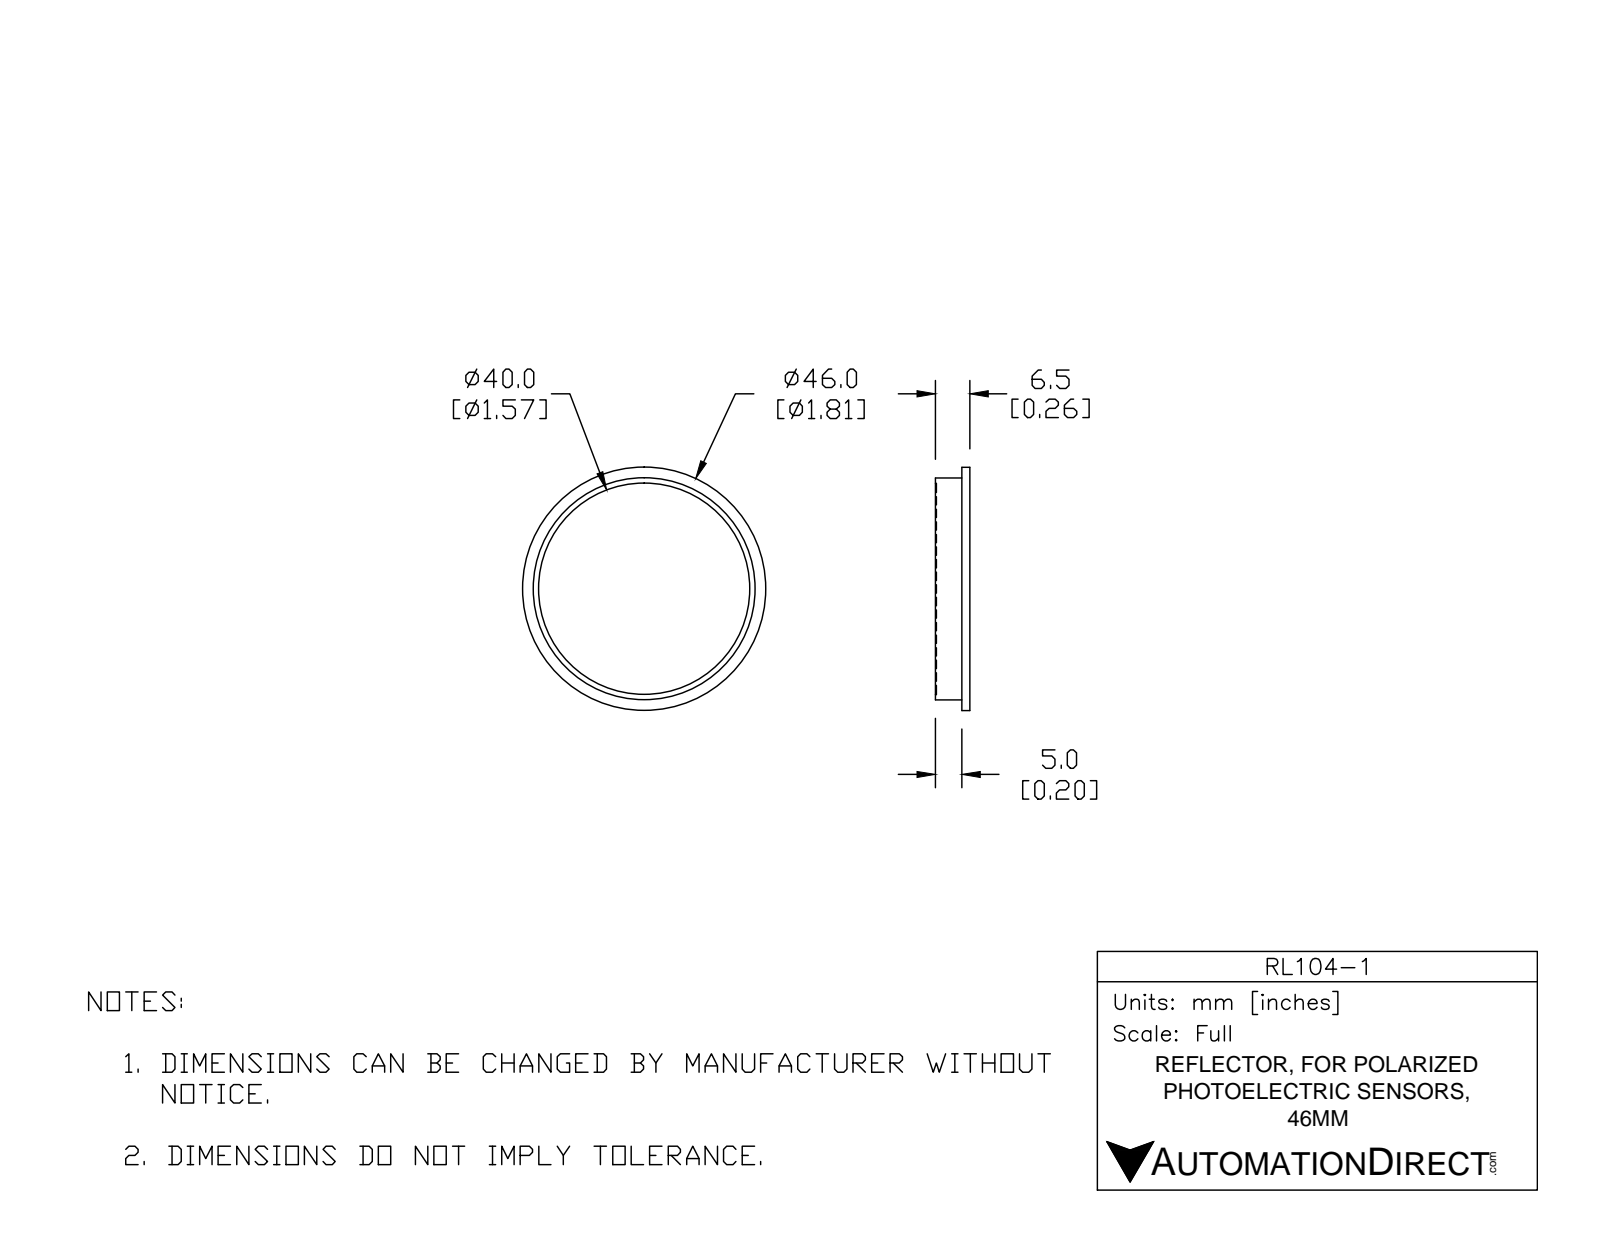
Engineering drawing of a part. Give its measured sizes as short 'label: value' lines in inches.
name: RL-104-1
written by: SolidWorks 2017 (AUTOMOTIVE_DESIGN)
unit: in
bodies: 1 solid, 10 faces (4 planar, 6 cylindrical, 0 other)
size: 1.811 × 1.811 × 0.256
volume: 0.56 in³; area: 6.549 in²
holes: 1× ⌀1.575
bosses: 1× ⌀1.811, 1× ⌀1.654
face distances: 0.248, 0.059, 0.189, 0.256, 0.197
